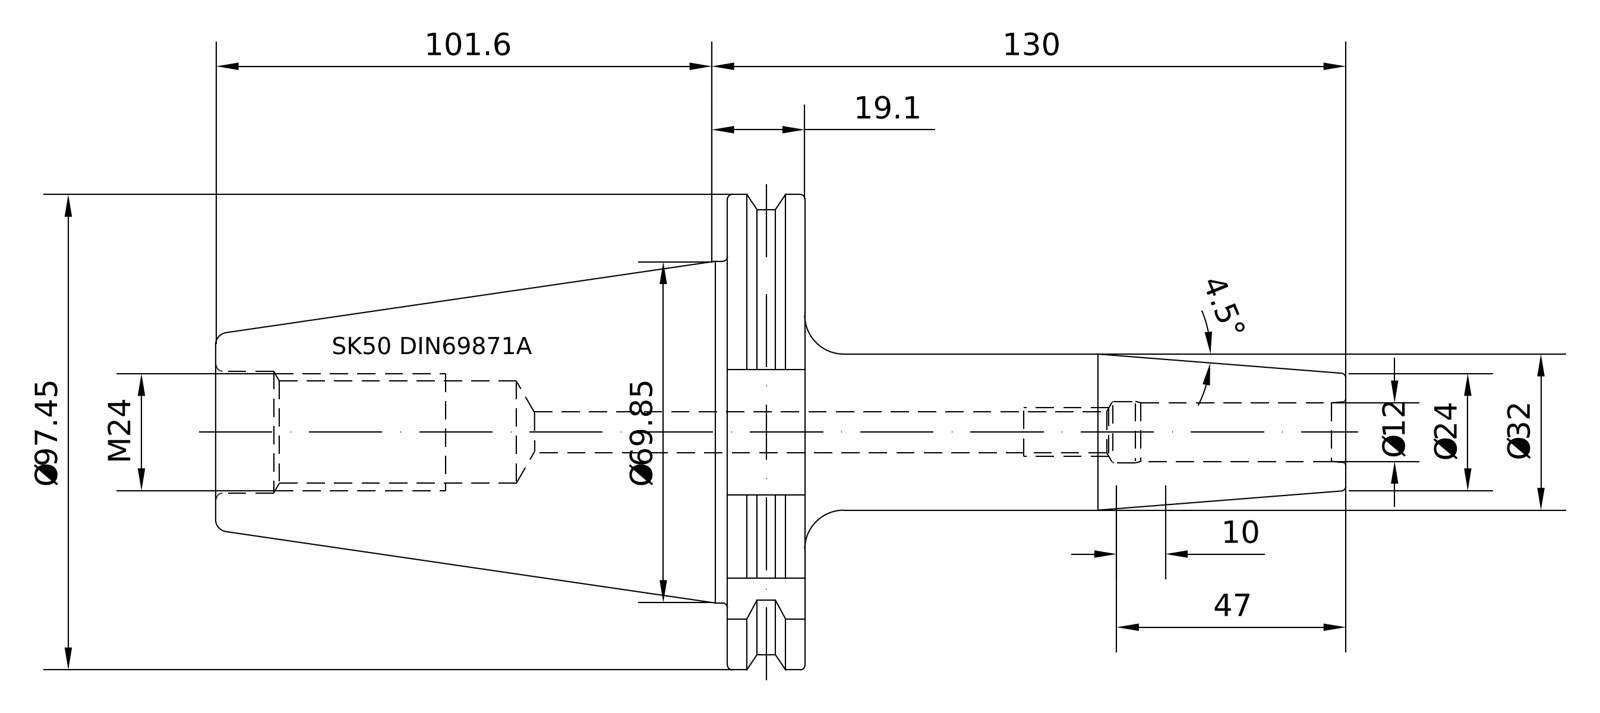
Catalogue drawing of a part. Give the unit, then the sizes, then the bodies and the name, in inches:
Units: inches
Overall size (bounding box): 9.118 × 3.837 × 3.701
Round holes (diameter × count): ⌀0.472 ×1, ⌀0.817 ×1, ⌀0.985 ×1, ⌀1.012 ×1
Round bosses / shafts (diameter × count): ⌀3.583 ×1, ⌀2.722 ×1, ⌀1.26 ×1, ⌀0.945 ×1
Partial cylindrical surfaces — rounded edges, fillets, slot ends (radius × count): R0.069 ×1, R1.919 ×1
Main face-to-face distances: 0.624, 2.866, 4.126, 4.75, 1.016, 9.118, 4.992, 4.368, 1.89, 2.236
Volume: 25.48 in³ · Surface area: 83.87 in²
Bodies: 1 solid, 93 faces (21 planar, 24 cylindrical, 48 other)
Part name (STEP PRODUCT): 50-444-12
STEP written by: PRO/ENGINEER BY PARAMETRIC TECHNOLOGY CORPORATION, 2010430 (CONFIG_CONTROL_DESIGN)
